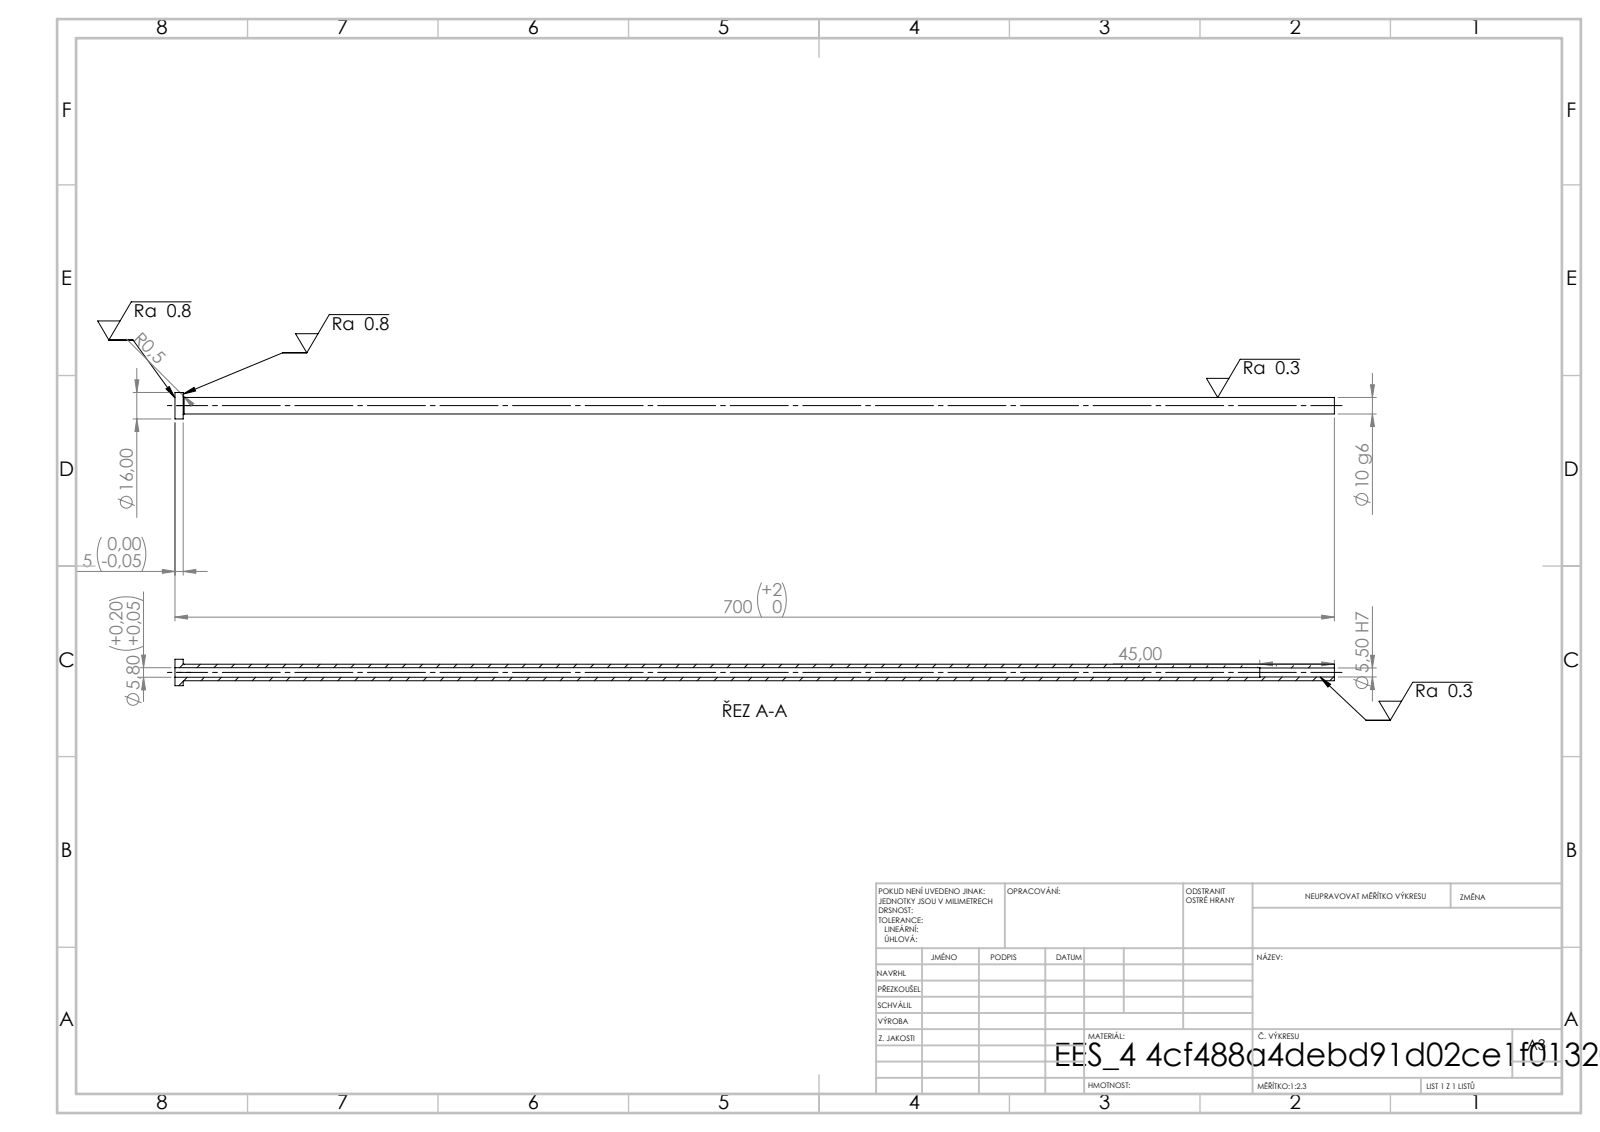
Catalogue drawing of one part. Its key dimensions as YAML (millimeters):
step_written_by: "SolidWorks 2019 (CONFIG_CONTROL_DESIGN)"
units: millimeters
bodies: {solids: 1, faces: 14, planar: 4, cylindrical: 8, other: 2}
overall_size: [700, 16, 16]
volume: 37217
surface_area: 35146
round_holes:
  - {diameter: 5.5, count: 1}
  - {diameter: 5.8, count: 1}
round_bosses_or_shafts:
  - {diameter: 16, count: 1}
  - {diameter: 10, count: 1}
face_to_face_distances: [5, 700, 695, 655, 650, 45]
